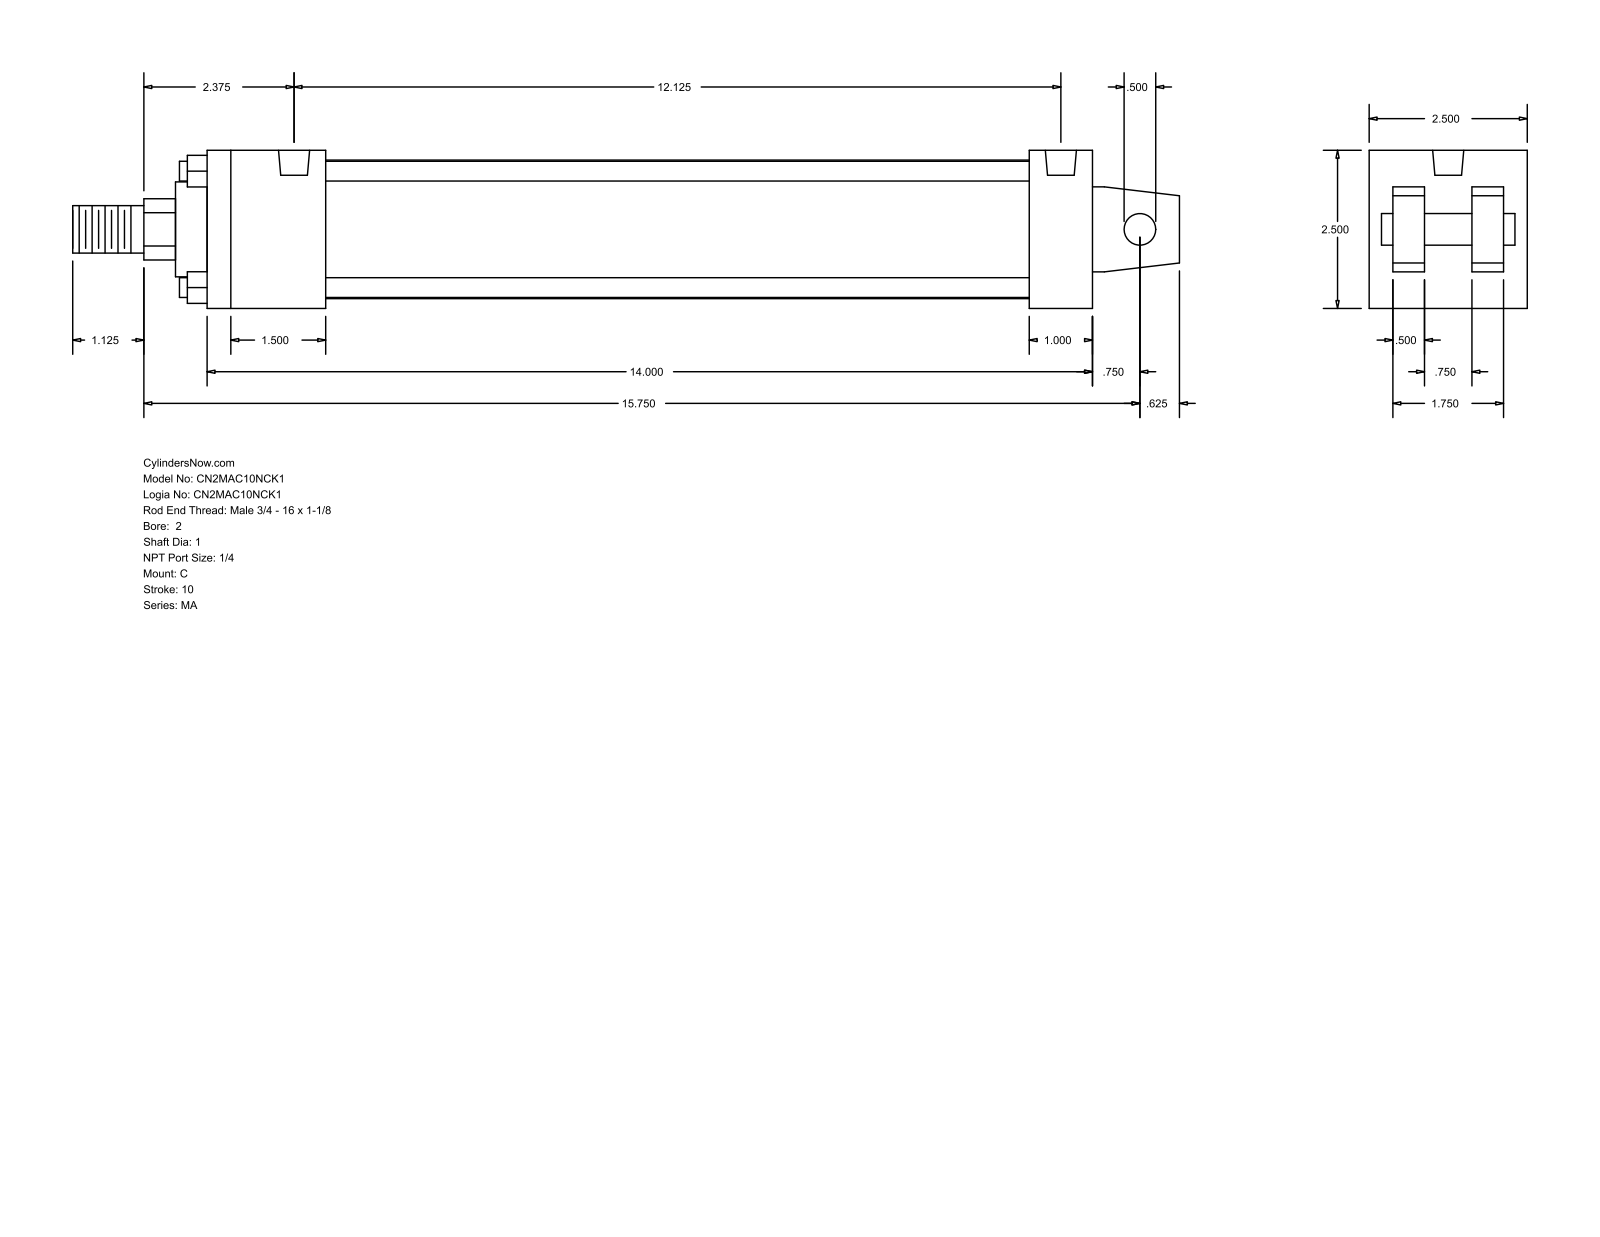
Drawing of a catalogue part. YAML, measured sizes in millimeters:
part_name: "MA_C__0200_1"
step_written_by: "GSSL Pune (CONFIG_CONTROL_DESIGN)"
units: millimeters
bodies: {solids: 0, faces: 103, planar: 76, cylindrical: 27, other: 0}
overall_size: [444.5, 63.5, 63.5]
round_holes:
  - {diameter: 7.94, count: 4}
  - {diameter: 12.49, count: 2}
round_bosses_or_shafts:
  - {diameter: 7.94, count: 4}
  - {diameter: 55.63, count: 1}
  - {diameter: 38.1, count: 1}
  - {diameter: 25.4, count: 1}
  - {diameter: 19.05, count: 1}
  - {diameter: 12.7, count: 1}
partial_cylinders:
  - {radius: 12.29, count: 1}
face_to_face_distances: [63.5, 12.7, 355.6, 22.22, 41.28, 9.52, 53.98, 31.76, 47.63, 25.4]
hole_center_spacings: [307.97]
